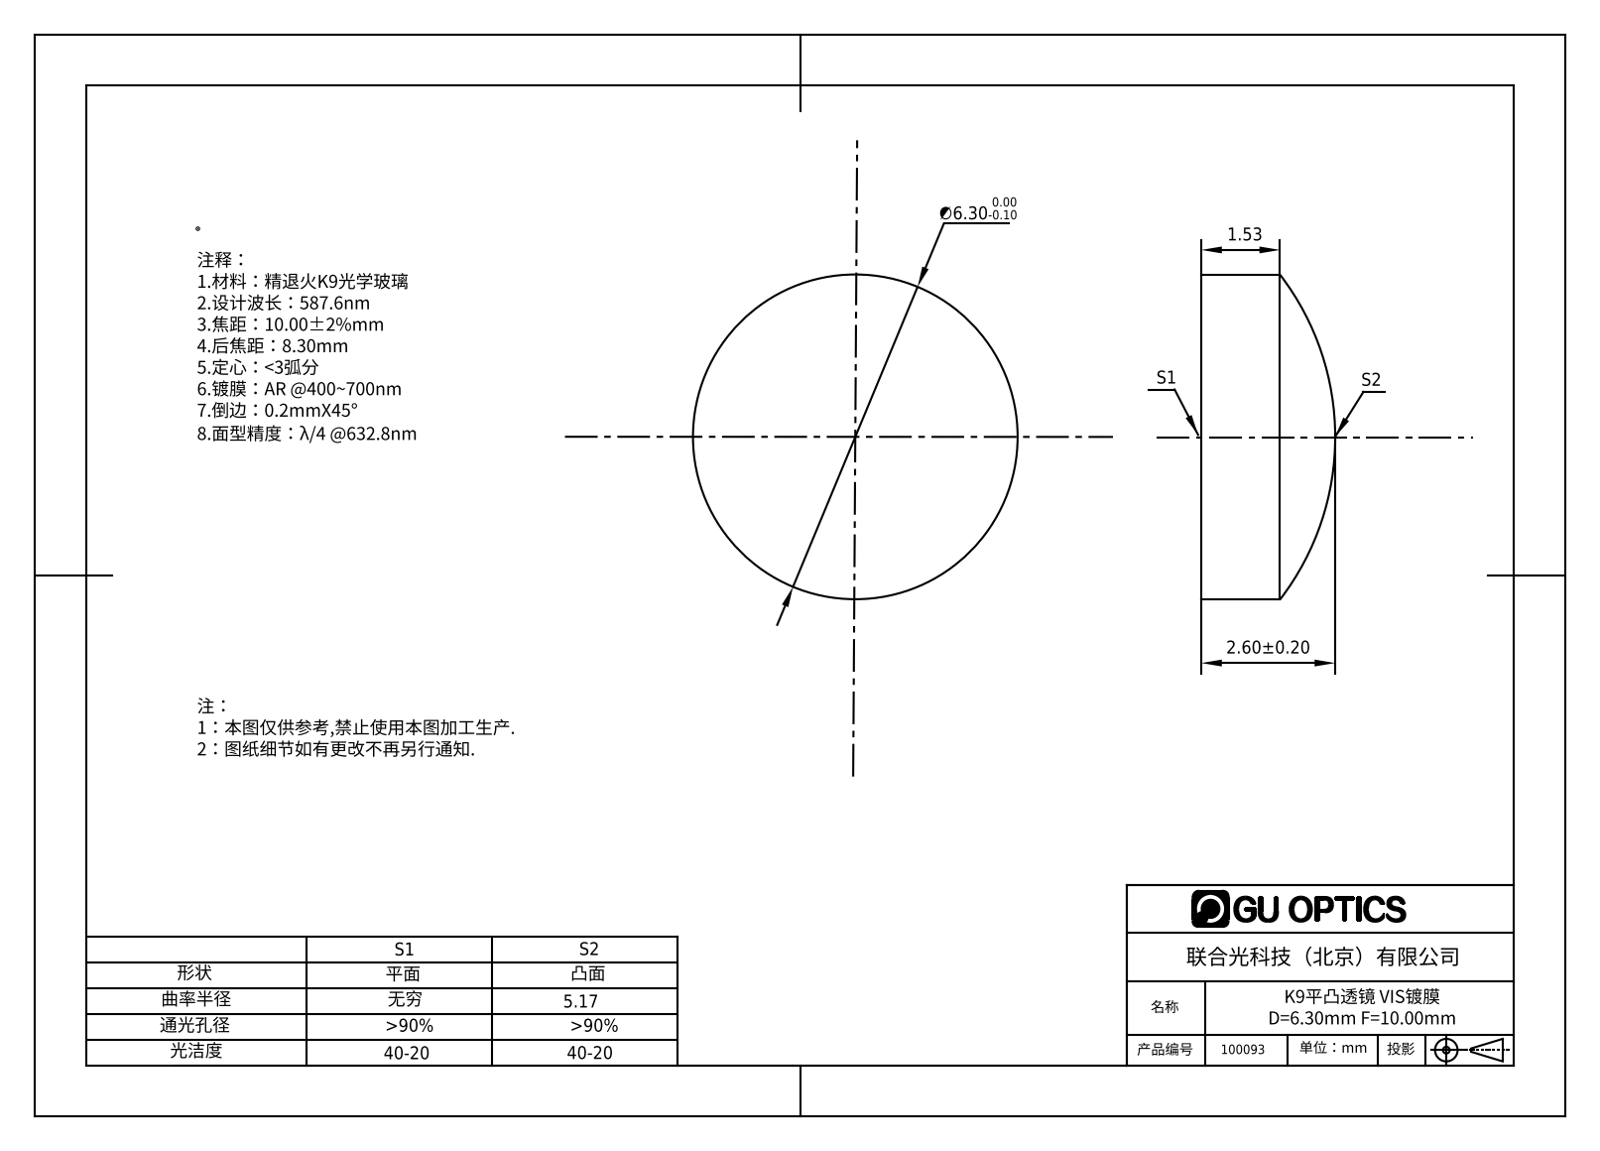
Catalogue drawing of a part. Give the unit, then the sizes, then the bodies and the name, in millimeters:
Units: millimetres
Overall size (bounding box): 6.3 × 6.3 × 2.6
Round bosses / shafts (diameter × count): ⌀6.3 ×1
Volume: 65 mm³ · Surface area: 96 mm²
Bodies: 1 solid, 5 faces (1 planar, 2 cylindrical, 2 other)
Part name (STEP PRODUCT): 100093
STEP written by: SolidWorks 2016 (AUTOMOTIVE_DESIGN)
